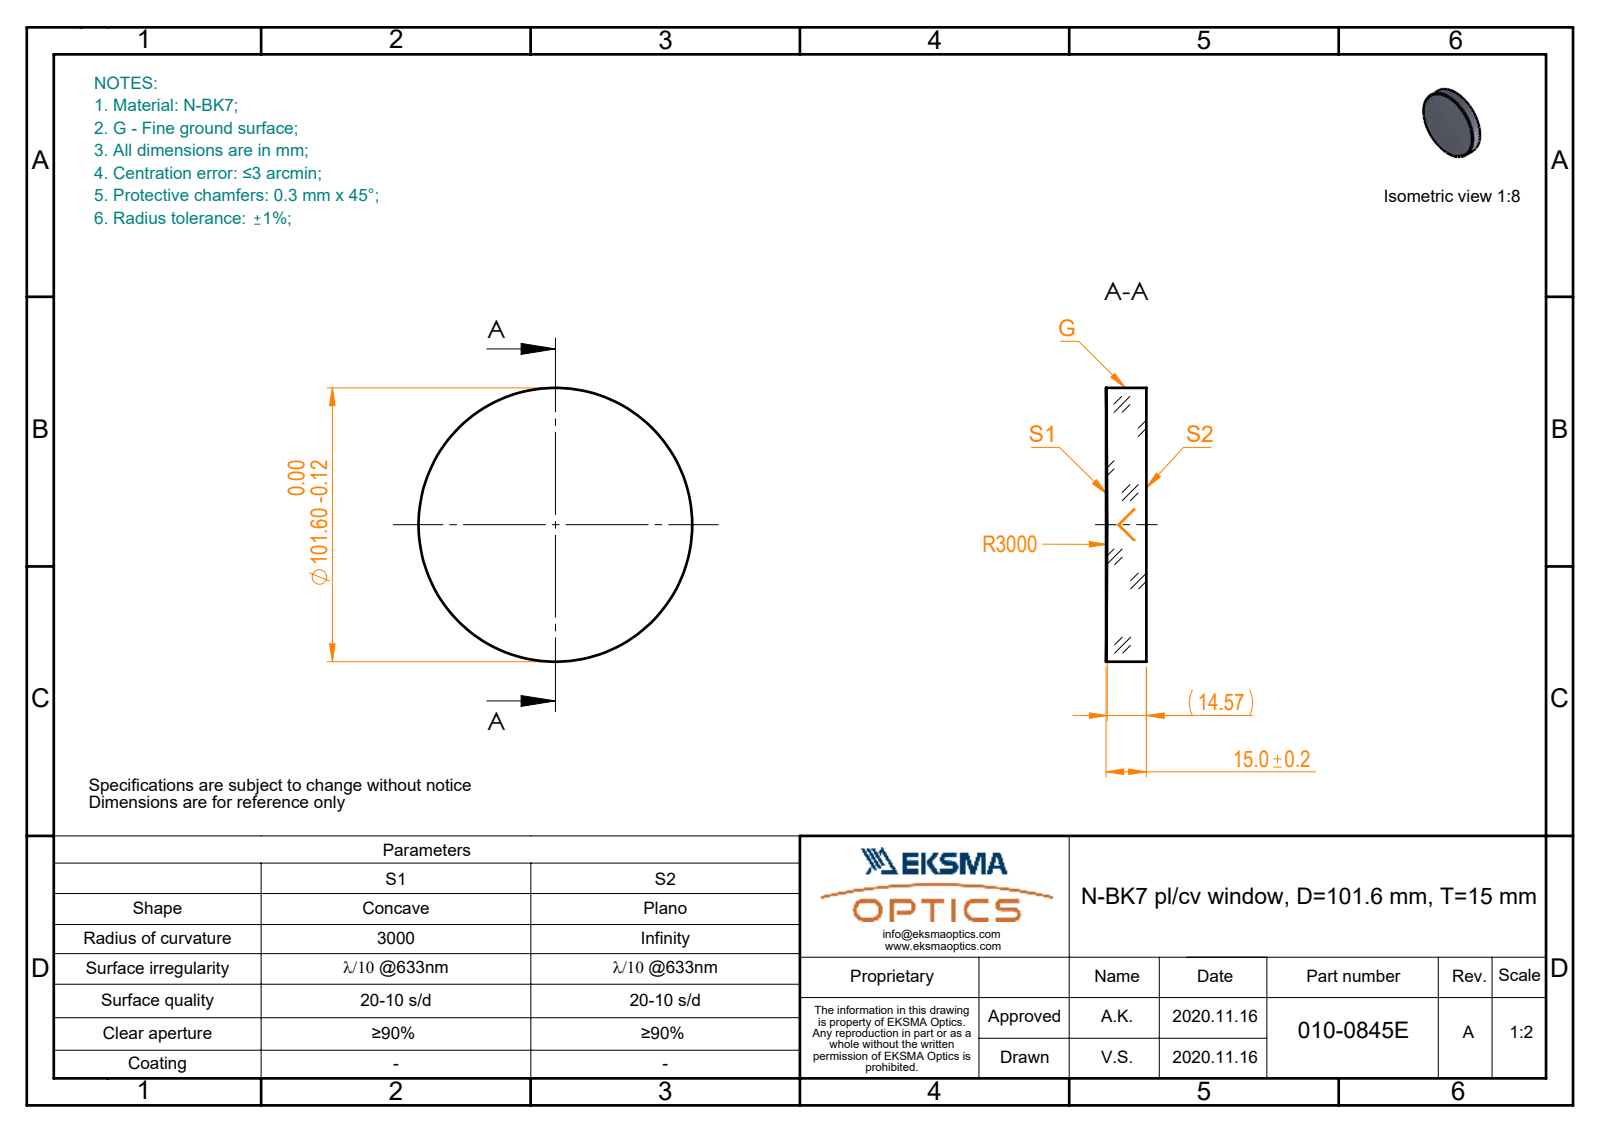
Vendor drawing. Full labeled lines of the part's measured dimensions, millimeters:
Part name (STEP PRODUCT): 010-0845E_N-BK7_PCV_window
STEP written by: SolidWorks 2019 (CONFIG_CONTROL_DESIGN)
Units: millimetres
Bodies: 1 solid, 5 faces (1 planar, 2 cylindrical, 2 other)
Overall size (bounding box): 101.6 × 101.6 × 15
Volume: 119 866 mm³ · Surface area: 21 003 mm²
Round bosses / shafts (diameter × count): ⌀101.6 ×1
